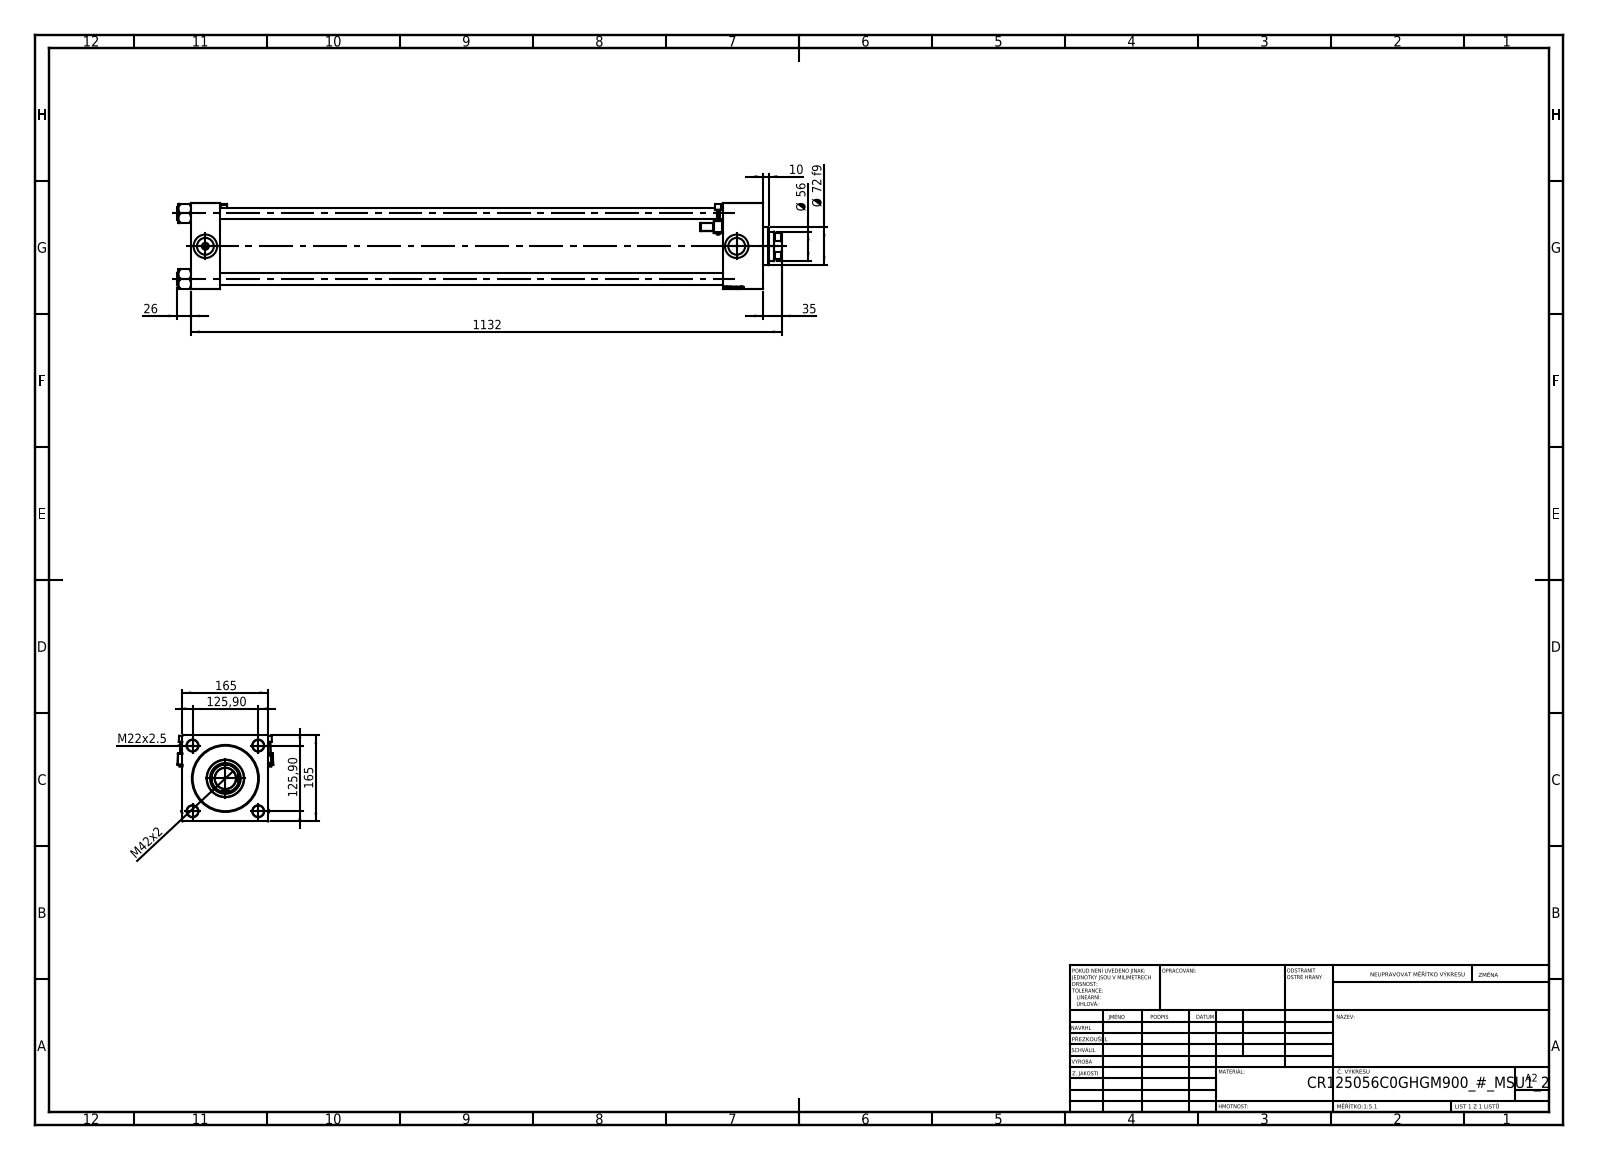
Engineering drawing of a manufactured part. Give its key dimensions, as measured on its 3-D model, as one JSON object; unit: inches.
{"part_name": "NUT_M5_C; V215CR_VCP_C; V215_VC_A; V215CR_C_TYCINKA (+2 more)", "step_written_by": "SolidWorks 2019 (CONFIG_CONTROL_DESIGN)", "units": "inches", "bodies": {"solids": 13, "faces": 1350, "planar": 632, "cylindrical": 146, "other": 572}, "overall_size": [45.591, 7.224, 6.496], "volume_in3": 555.5, "surface_area_in2": 2514, "round_holes": [[0.866, 4], [0.276, 2], [1.269, 2], [1.772, 2], [1.594, 1], [2.205, 1], [2.323, 1], [3.78, 1], [4.921, 1], [4.941, 1]], "round_bosses_or_shafts": [[0.984, 4], [0.236, 2], [5.157, 1], [2.835, 1]], "partial_cylinders_radius": [[0.02, 48], [0.039, 2], [0.098, 2], [0.157, 2], [1.063, 1]], "face_to_face_distances": [6.496, 2.165, 41.024, 43.189, 40.118, 37.953, 3.071, 42.059, 39.894, 1.941], "hole_center_spacings": [3.505, 4.957, 7.01, 40.098]}
